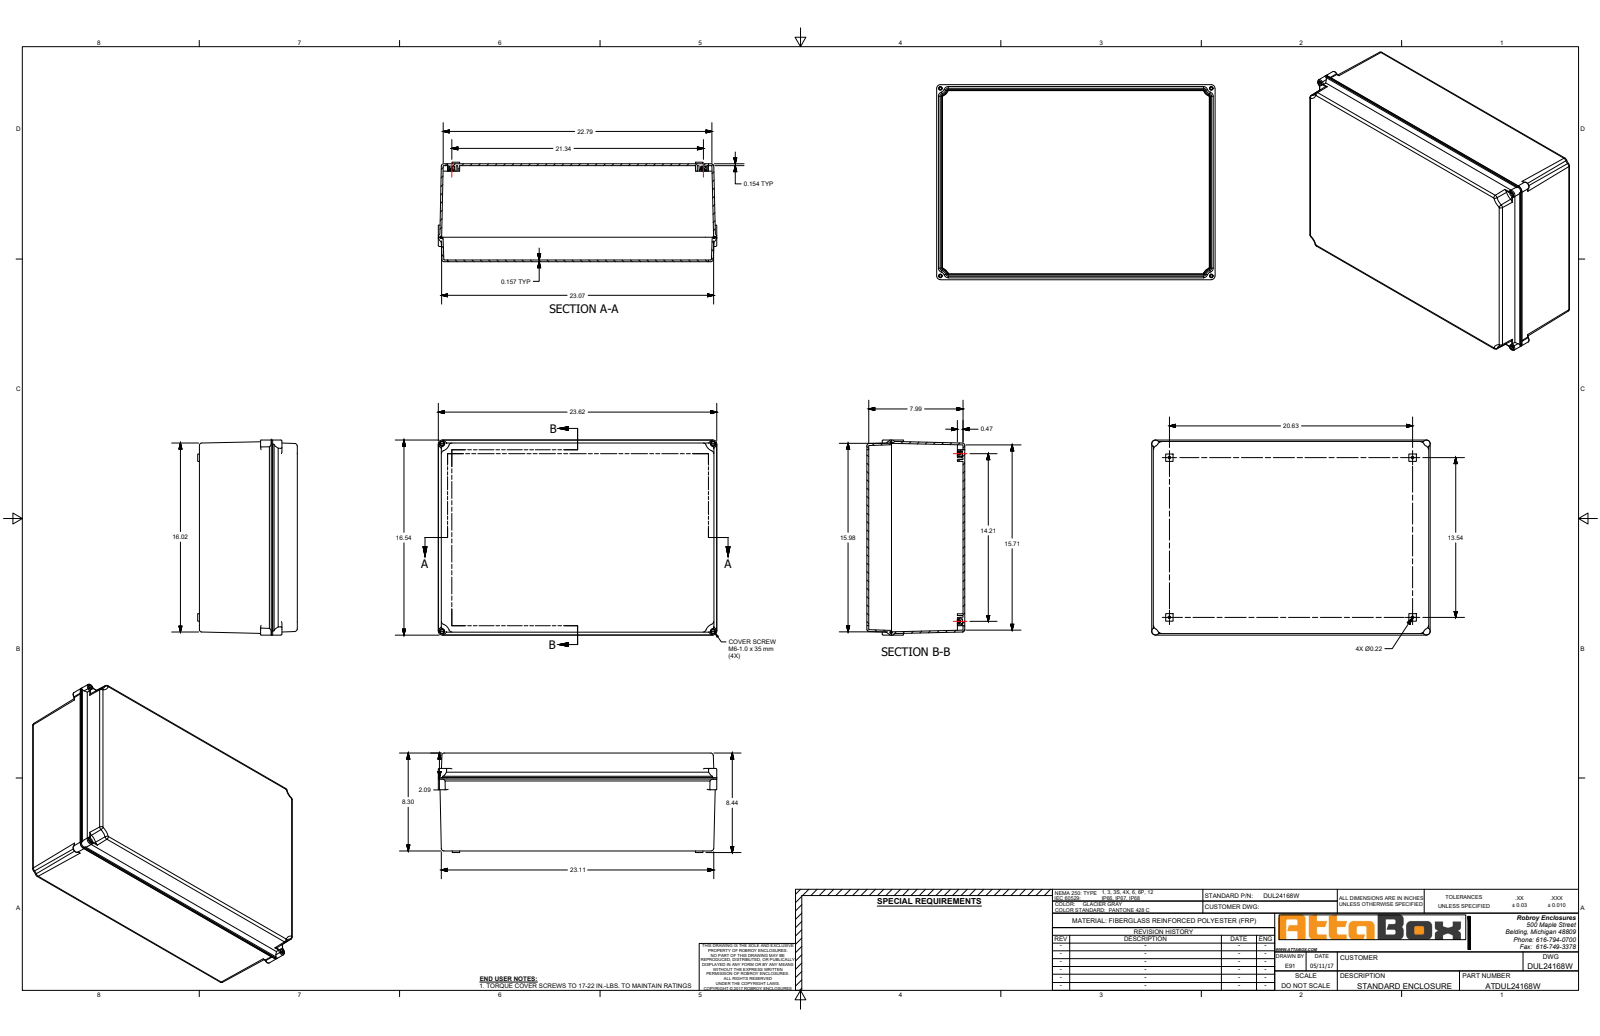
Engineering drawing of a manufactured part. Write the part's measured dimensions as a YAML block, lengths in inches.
part_name: "DUL24168W"
step_written_by: "SolidWorks 2018 (AUTOMOTIVE_DESIGN)"
units: inches
bodies: {solids: 15, faces: 758, planar: 270, cylindrical: 208, other: 280}
overall_size: [23.622, 16.535, 8.441]
volume: 224.6
surface_area: 2862
round_holes:
  - {diameter: 0.163, count: 4}
  - {diameter: 0.194, count: 4}
  - {diameter: 0.197, count: 4}
  - {diameter: 0.217, count: 4}
  - {diameter: 0.26, count: 4}
round_bosses_or_shafts:
  - {diameter: 0.433, count: 4}
  - {diameter: 0.374, count: 4}
  - {diameter: 0.315, count: 4}
  - {diameter: 0.236, count: 4}
partial_cylinders:
  - {radius: 0.02, count: 28}
  - {radius: 0.039, count: 20}
  - {radius: 0.335, count: 12}
  - {radius: 0.079, count: 8}
  - {radius: 0.197, count: 8}
  - {radius: 0.217, count: 8}
  - {radius: 0.217, count: 8}
  - {radius: 0.315, count: 8}
face_to_face_distances: [0.157, 0.154, 8.146, 7.992, 8.303, 8.15, 0.162, 0.162, 6.217, 6.063]
hole_center_spacings: [0.487, 1.183, 1.67, 13.882, 14.772, 15.082, 20.987, 21.843]
